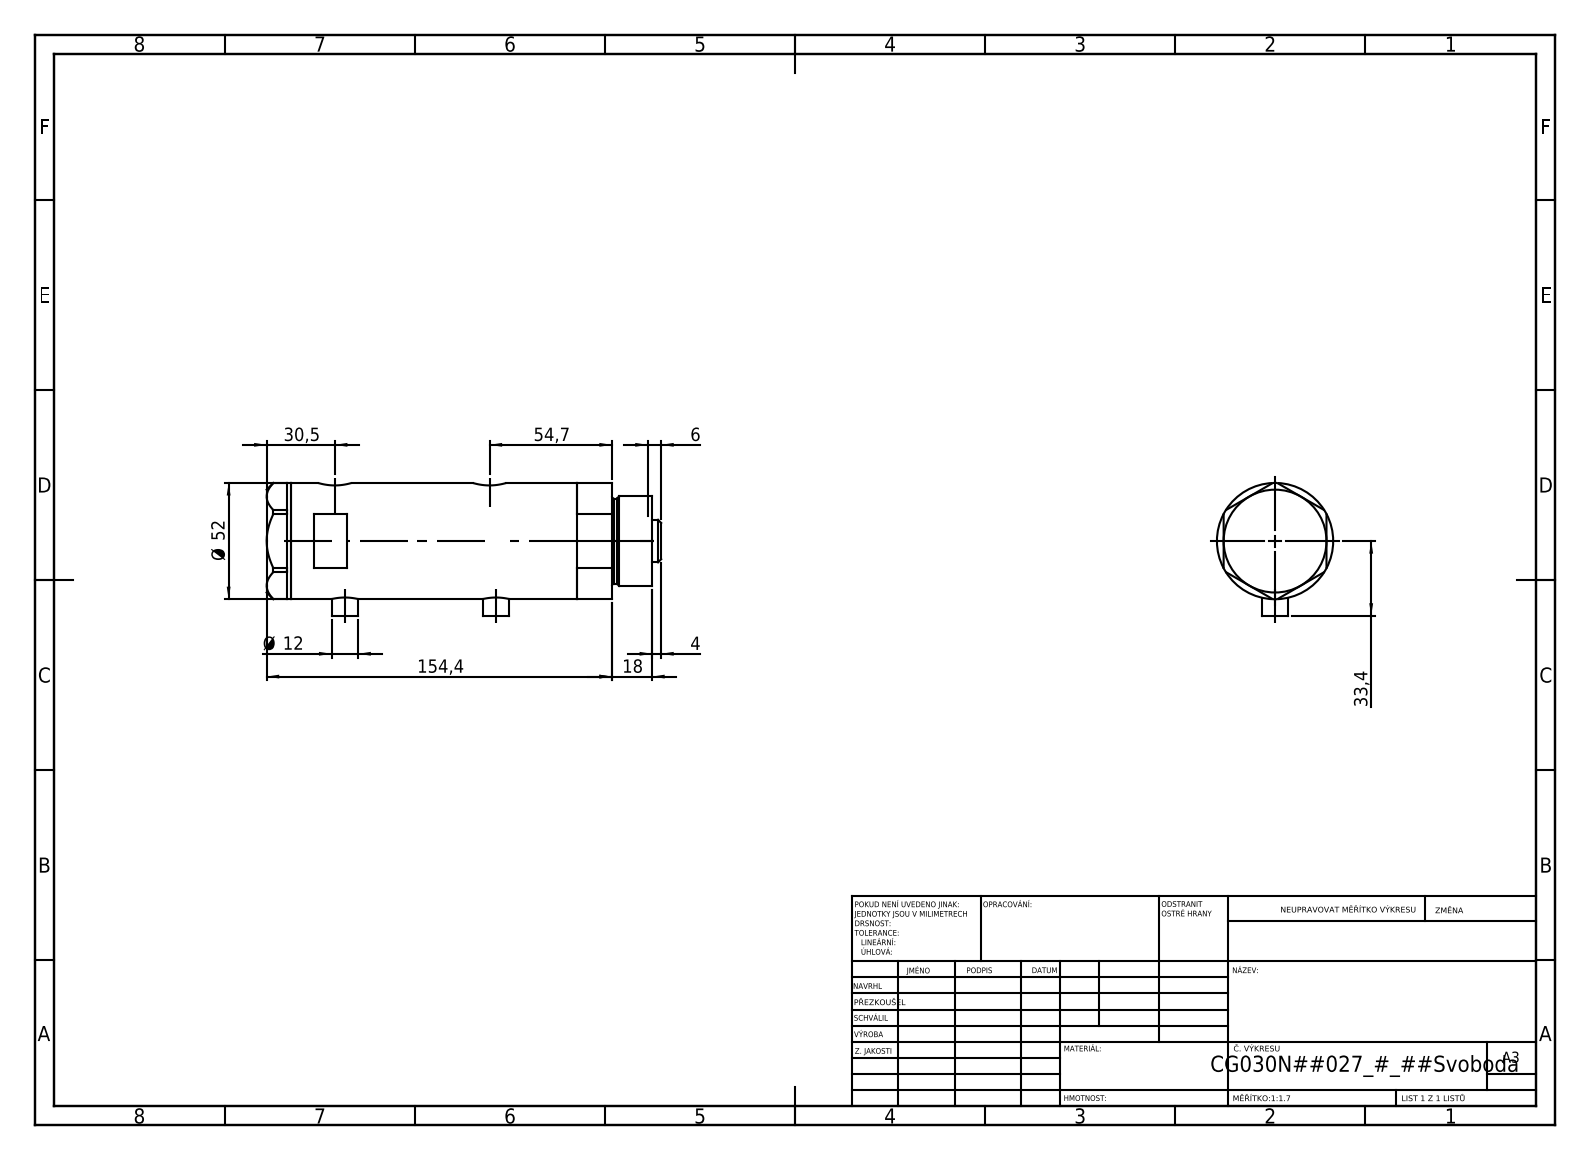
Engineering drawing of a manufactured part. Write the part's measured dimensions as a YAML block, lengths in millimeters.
part_name: "V270CG_BACK; V270CG_FRONT; V270CG_VC; V270CG_MIDDLE"
step_written_by: "SolidWorks 2019 (CONFIG_CONTROL_DESIGN)"
units: millimeters
bodies: {solids: 4, faces: 140, planar: 67, cylindrical: 53, other: 20}
overall_size: [176.45, 59.4, 52]
volume: 329839
surface_area: 76872
round_holes:
  - {diameter: 5, count: 2}
  - {diameter: 9.73, count: 2}
  - {diameter: 12.5, count: 2}
  - {diameter: 15, count: 2}
  - {diameter: 6.5, count: 1}
  - {diameter: 20, count: 1}
  - {diameter: 21.5, count: 1}
  - {diameter: 30, count: 1}
  - {diameter: 33, count: 1}
  - {diameter: 44, count: 1}
round_bosses_or_shafts:
  - {diameter: 12, count: 2}
  - {diameter: 52, count: 1}
  - {diameter: 40, count: 1}
  - {diameter: 38, count: 1}
  - {diameter: 19, count: 1}
face_to_face_distances: [91.5, 23.8, 67.7, 11, 34.8, 102.5, 46, 138.9, 127.9, 104.1]
hole_center_spacings: [2.9, 4.5, 64.7, 67.6, 69.2, 72.1]
